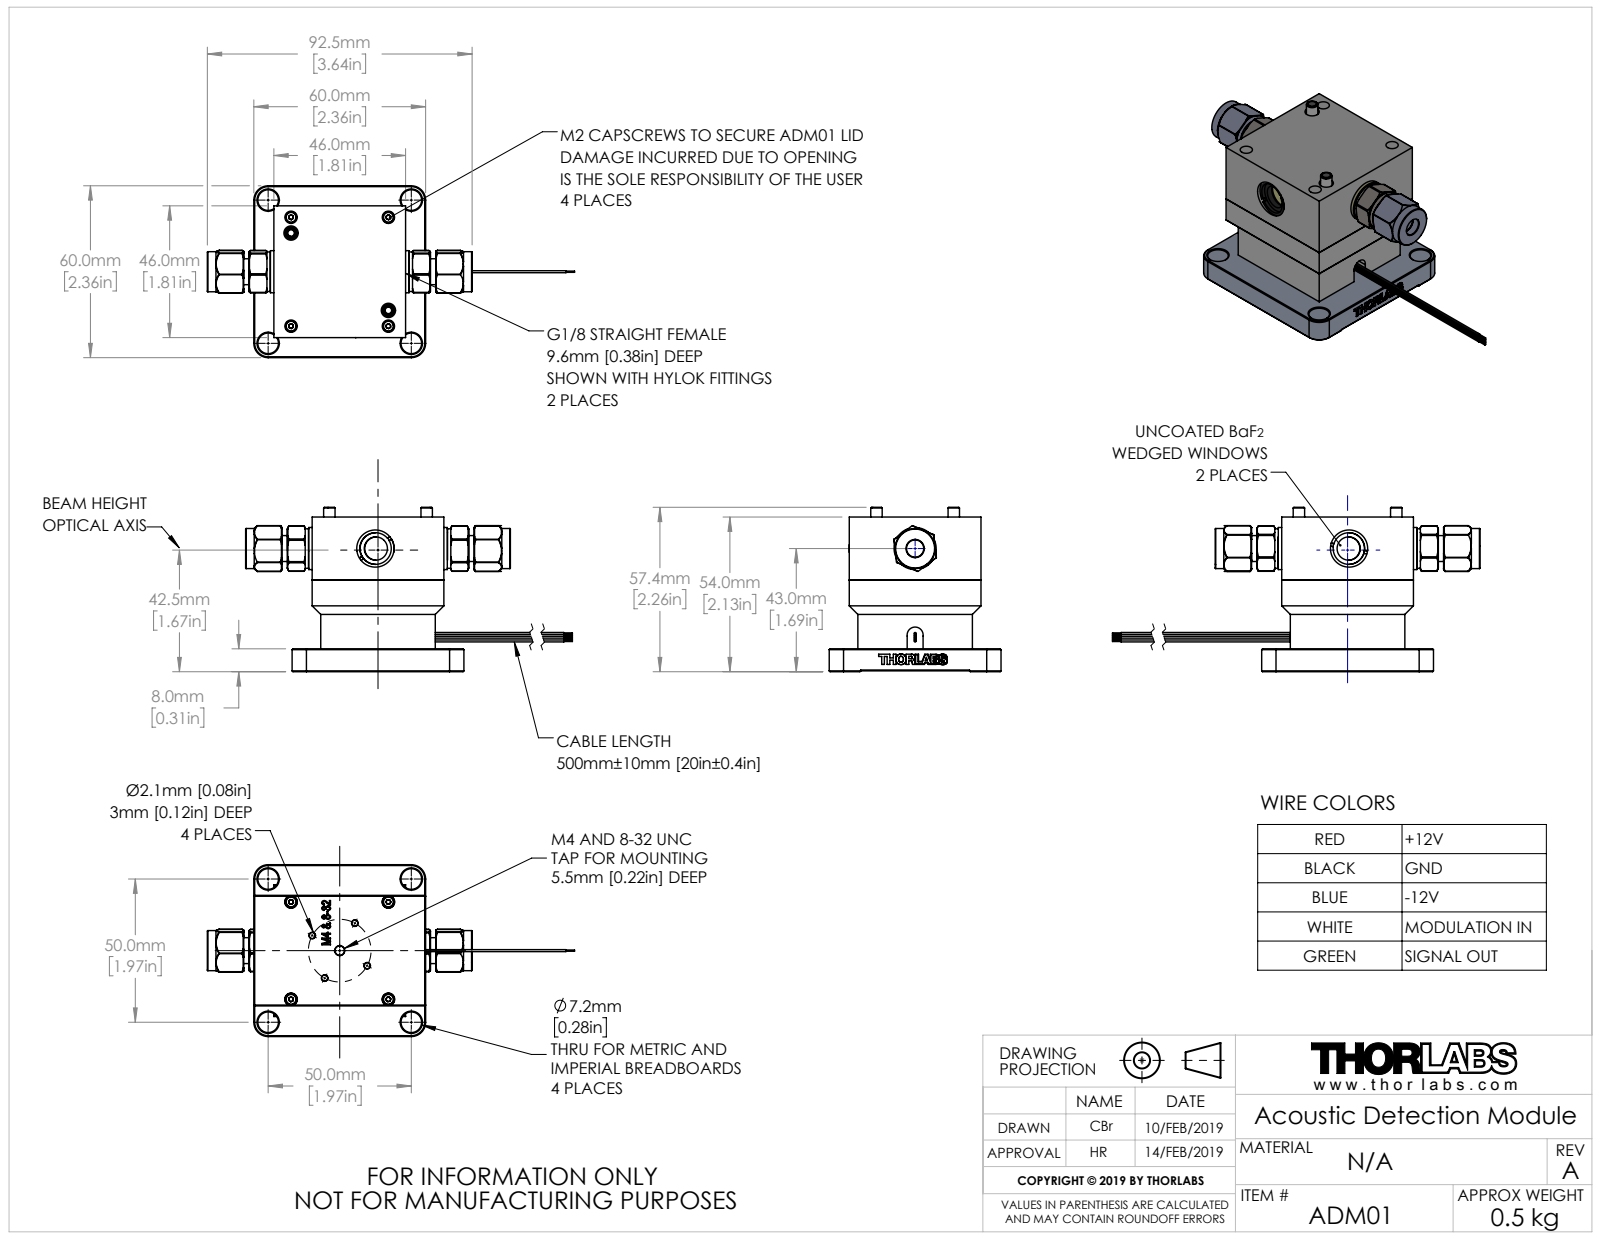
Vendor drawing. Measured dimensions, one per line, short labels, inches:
name: part_ADM01
written by: SolidWorks 2018 (AUTOMOTIVE_DESIGN)
unit: in
bodies: 59 solids, 2560 faces (1086 planar, 600 cylindrical, 874 other)
size: 3.868 × 2.362 × 2.26
volume: 6.044 in³; area: 83.02 in²
holes: 17× ⌀0.063, 8× ⌀0.087, 6× ⌀0.118, 4× ⌀0.083, 4× ⌀0.091, 4× ⌀0.165, 4× ⌀0.169, 4× ⌀0.283, 3× ⌀0.157, 3× ⌀0.197, 3× ⌀0.236, 2× ⌀0.039
bosses: 20× ⌀0.079, 14× ⌀0.15, 5× ⌀0.017, 4× ⌀0.157, 3× ⌀0.315, 2× ⌀0.535, 2× ⌀0.453, 2× ⌀0.355
rounds: 15× R0.007, 12× R0.02, 9× R0.007, 8× R0.043, 8× R0.079, 6× R0.059, 4× R0.012, 4× R0.047
face distances: 1.811, 0.945, 0.118, 0.276, 0.303, 1.248, 0.866, 2.114, 1.693, 1.575
hole spacings: 1.098, 0.459, 0.893, 1.004, 1.12, 1.339, 1.417, 0.079
